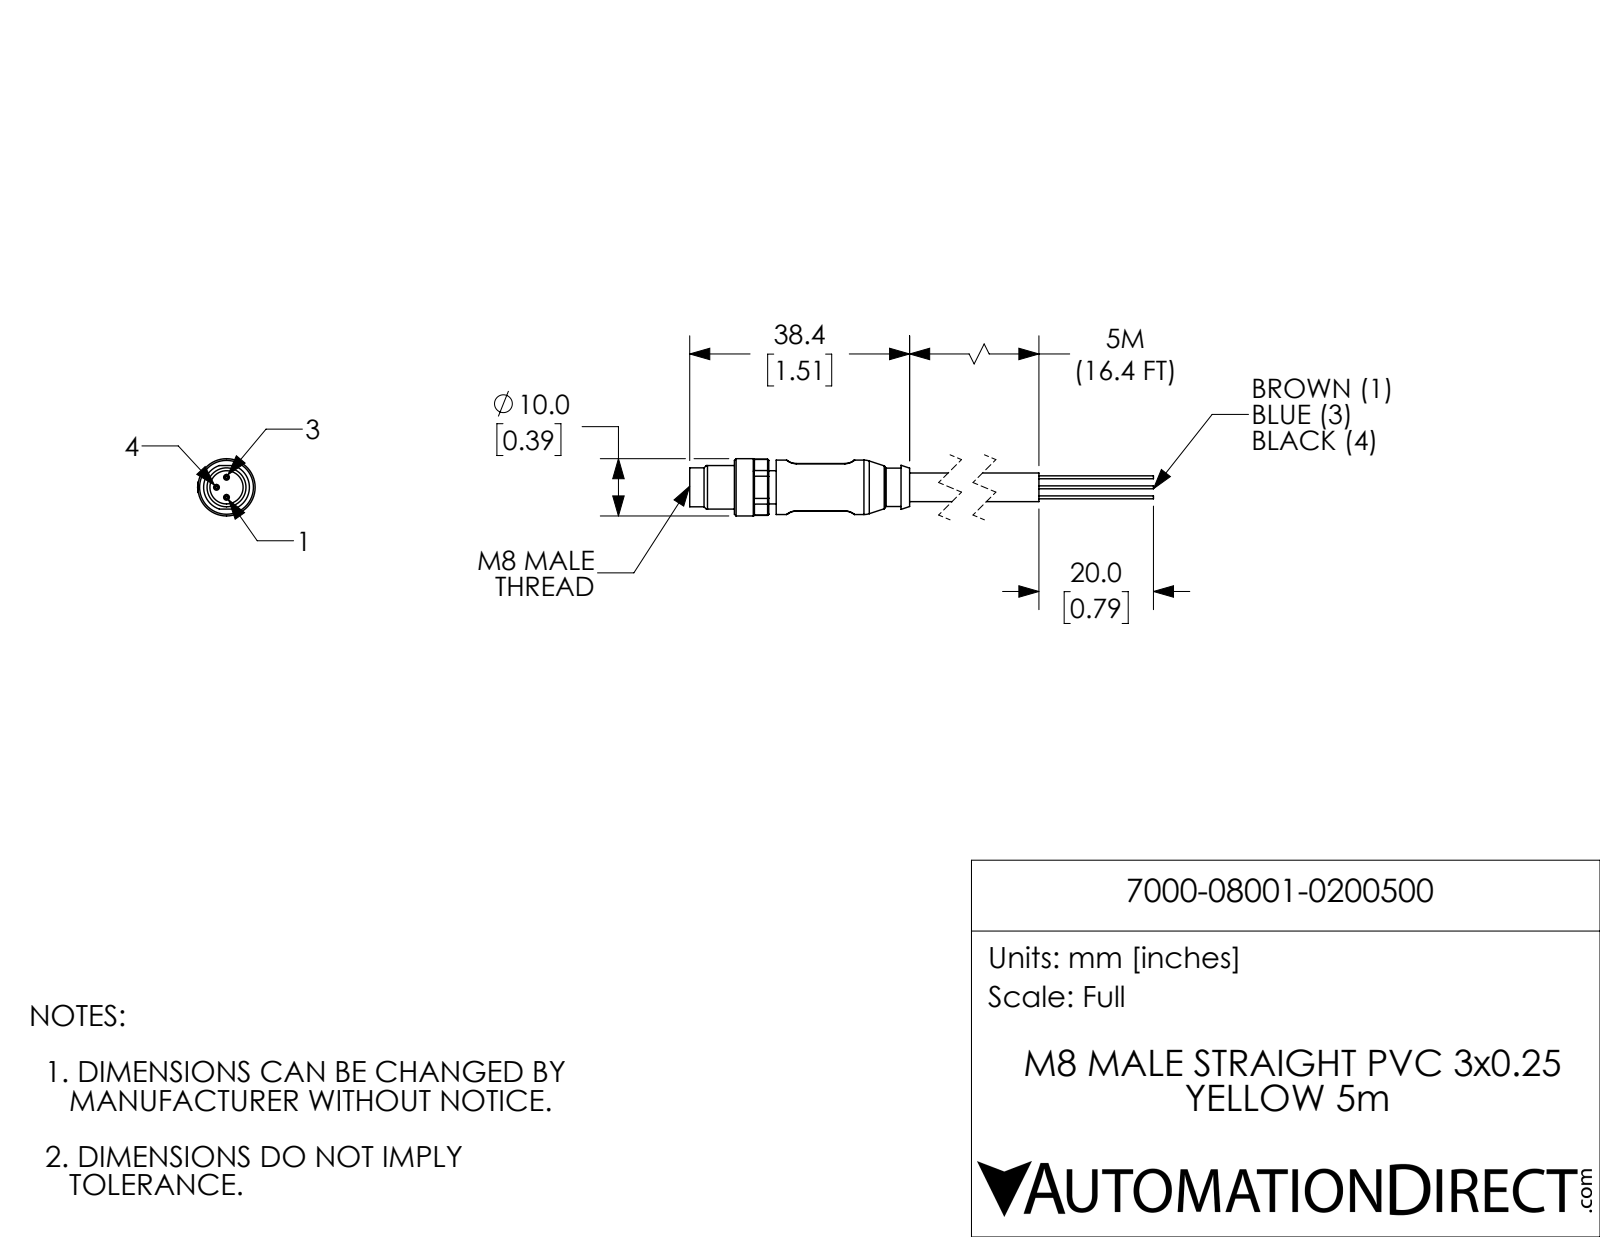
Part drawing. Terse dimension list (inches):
name: 7000-08001-0200500
written by: SolidWorks 2017 (AUTOMOTIVE_DESIGN)
unit: in
bodies: 4 solids, 119 faces (41 planar, 44 cylindrical, 34 other)
size: 3.087 × 0.396 × 0.394
volume: 0.155 in³; area: 2.792 in²
holes: 1× ⌀0.228
bosses: 3× ⌀0.039, 3× ⌀0.02, 1× ⌀0.394, 1× ⌀0.374, 1× ⌀0.315, 1× ⌀0.268, 1× ⌀0.264, 1× ⌀0.197
rounds: 4× R0.008, 4× R0.098, 1× R0.193, 1× R0.199
face distances: 0.327, 0.051, 0.354, 0.014, 0.313, 0.346, 0.398, 2.102, 1.756, 1.705
